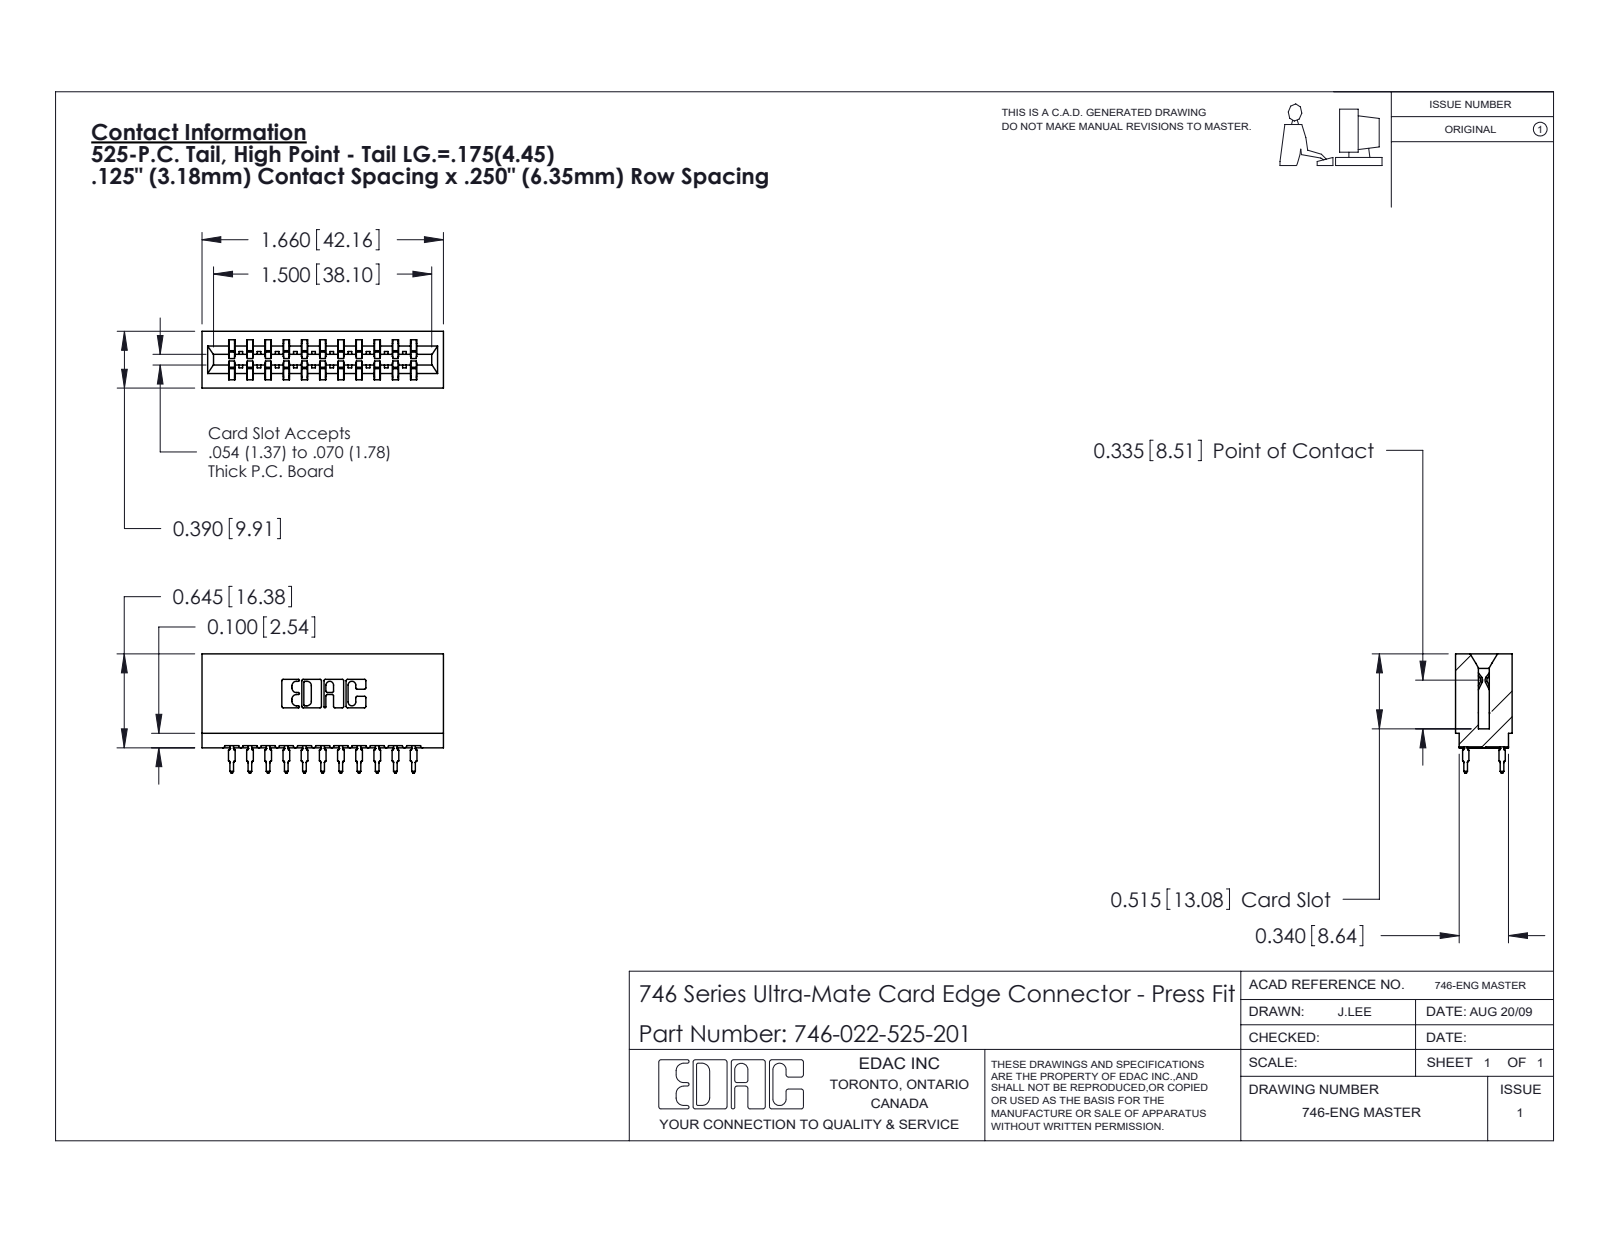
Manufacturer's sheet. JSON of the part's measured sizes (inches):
{"part_name": "746-292-001_525; 746 Part_.515 Slot Depth - 01; 746-022-525-201", "step_written_by": "SolidWorks 2020 (CONFIG_CONTROL_DESIGN)", "units": "inches", "bodies": {"solids": 23, "faces": 2066, "planar": 1067, "cylindrical": 427, "other": 572}, "overall_size": [1.66, 0.819, 0.39], "volume_in3": 0.287, "surface_area_in2": 10.67, "partial_cylinders_radius": [[0.021, 44], [0.01, 22], [0.015, 12], [0.005, 8], [0.011, 8], [0.007, 6], [0.031, 6], [0.026, 3]], "face_to_face_distances": [0.25, 0.333, 0.5, 0.057, 0.125, 0.125, 0.39, 0.042, 0.208, 0.083]}
